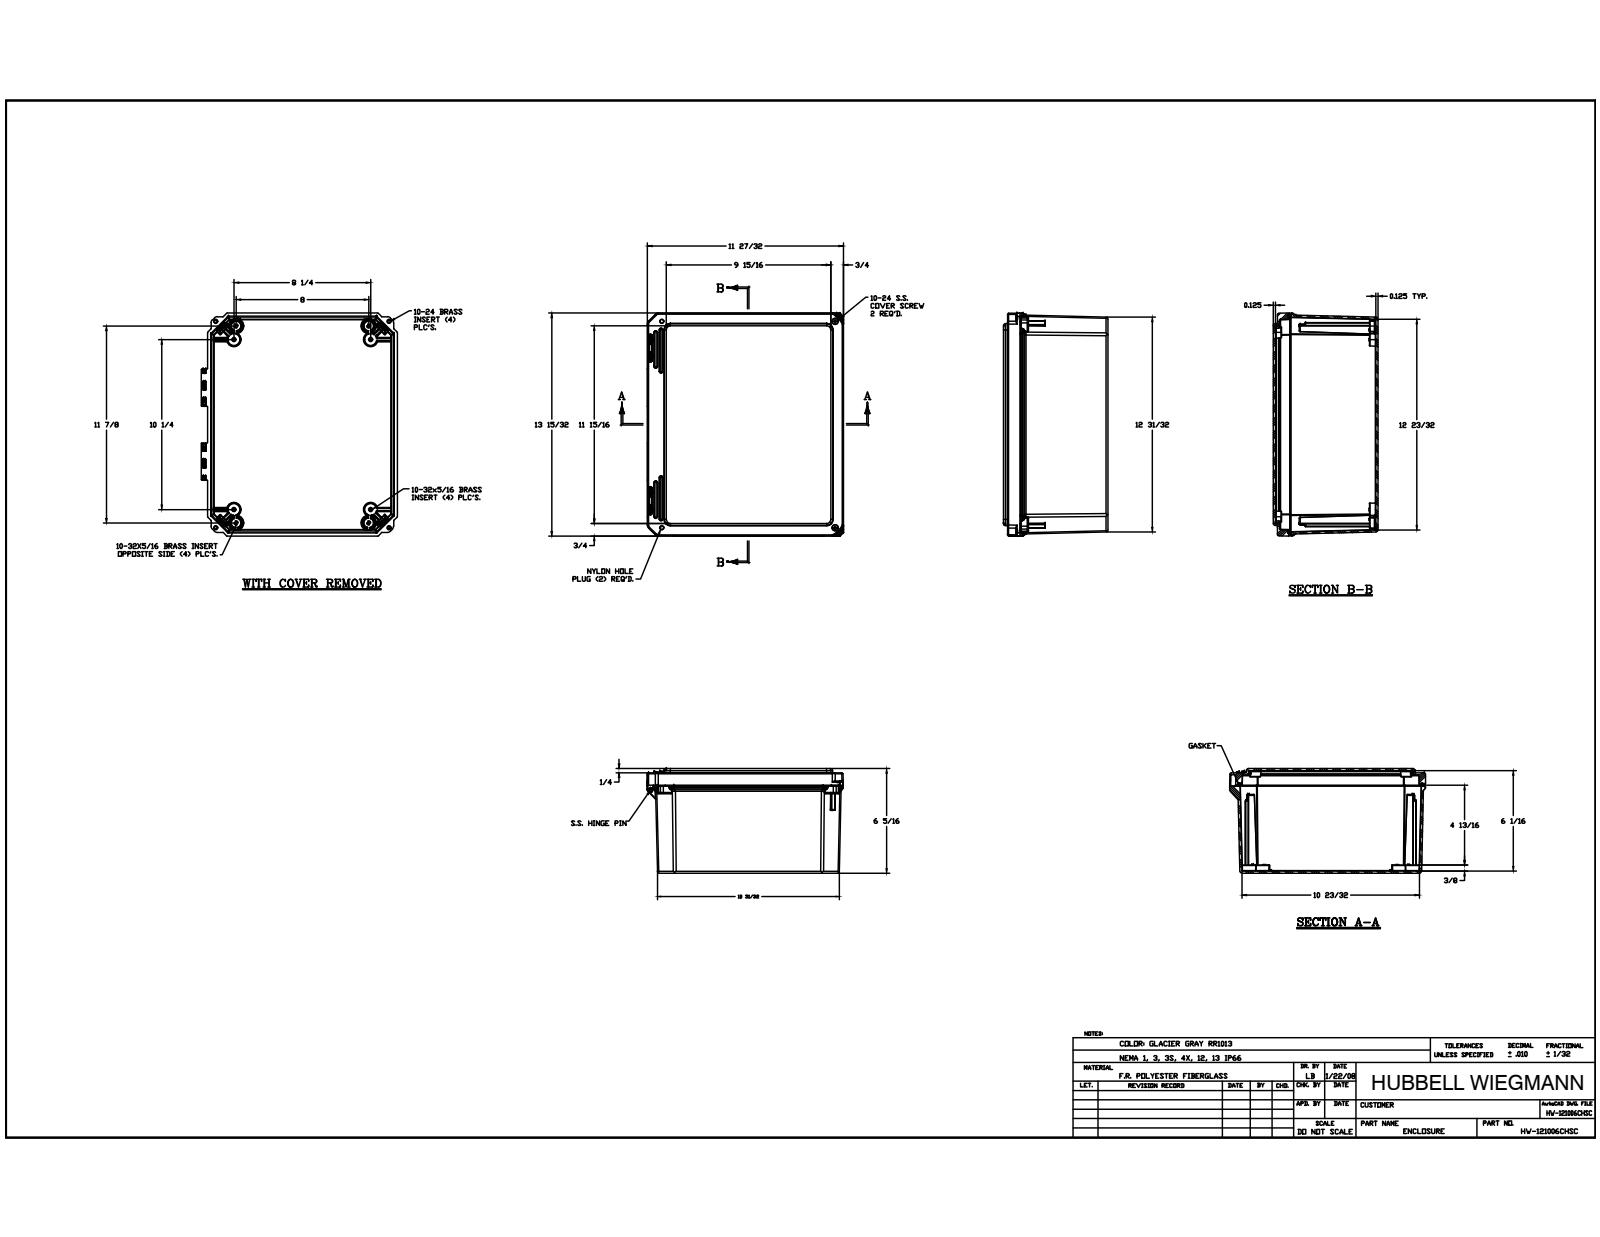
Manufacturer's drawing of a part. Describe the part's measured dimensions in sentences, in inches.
The part is named "DS121006BOX; BRASS INSERT-(; BRASS INSERT-(_1; BRASS INSERT-(_2 (+8 more)". Its 3-D file was written by "Autodesk Inventor 2014 (AUTOMOTIVE_DESIGN)". It is 29 solids with 2243 faces: 713 planar, 864 cylindrical and 666 other. Overall it measures 13.456 by 11.831 by 6.31 inches. Its volume is 93.55 cubic inches and its surface area 1 277 square inches. Round holes: 16 of diameter 0.156, 8 of diameter 0.152, 4 of diameter 0.252, 4 of diameter 0.253, 2 of diameter 0.15, 2 of diameter 0.219, 2 of diameter 0.227, 2 of diameter 0.313, 1 of diameter 0.137. Round bosses or shafts: 16 of diameter 0.246, 4 of diameter 0.87, 2 of diameter 0.45, 2 of diameter 0.435, 2 of diameter 0.209, 2 of diameter 0.199, 1 of diameter 0.135. Partial cylindrical surfaces (rounded edges, fillets, slot ends): 203 of radius 0.01, 84 of radius 0.02, 80 of radius 0.005, 45 of radius 0.03, 26 of radius 0.063, 24 of radius 0.03, 24 of radius 0.09, 24 of radius 0.096. The main face-to-face distances are 0.125, 6.185, 6.31, 6.061, 0.139, 0.14, 0.14, 0.25, 5.935, 0.125. The hole center spacings are 0.824, 10.692, 11.065, 11.406, 11.406, 13.727, 0.946, 1.261.
